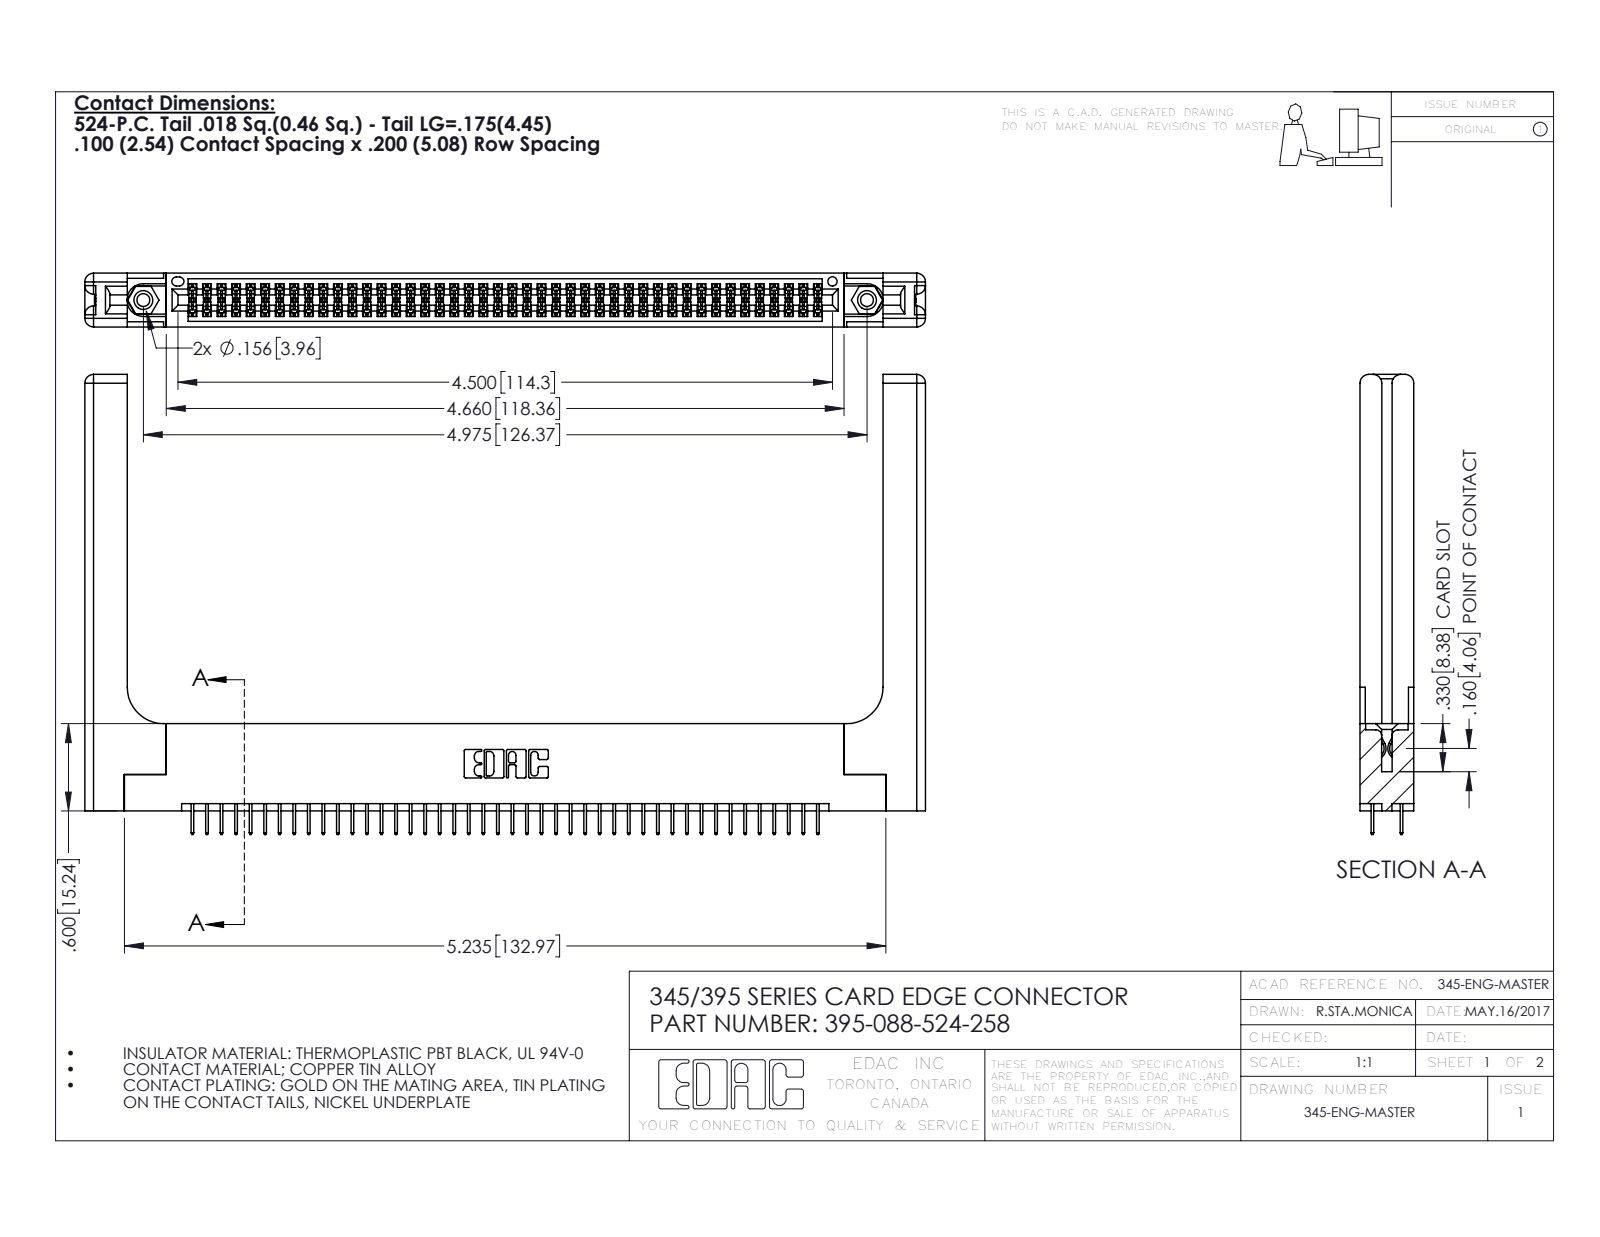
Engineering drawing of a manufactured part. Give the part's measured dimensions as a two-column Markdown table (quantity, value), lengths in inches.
| quantity | value |
| --- | --- |
| part name | 395-088-524-258; 345 Part_Flush Mounting Lugs - 0.156 Dia-TH; 345-292-001_345-293-124; 345-250-001_345-250-001-102 (+1 more) |
| STEP written by | SolidWorks 2016 (CONFIG_CONTROL_DESIGN) |
| units | inches |
| bodies | 93 solids, 5134 faces (3660 planar, 1414 cylindrical, 60 other) |
| overall size | 5.779 × 3.162 × 0.37 |
| volume | 1.38 in³ |
| surface area | 39.76 in² |
| round holes (diameter × count) | 0.089 × 2, 0.125 × 2, 0.156 × 2, 0.064 × 1 |
| round bosses / shafts (diameter × count) | 0.155 × 2 |
| partial cylindrical surfaces (radius × count) | 0.006 × 132, 0.01 × 22, 0.06 × 16, 0.007 × 6, 0.031 × 6, 0.026 × 3, 0.014 × 2, 0.019 × 2 |
| main face-to-face distances | 0.072, 0.37, 0.298, 0.2, 0.098, 0.272, 0.025, 0.225, 0.148, 0.15 |
| hole center spacings | 0.27, 4.739, 4.975 |
